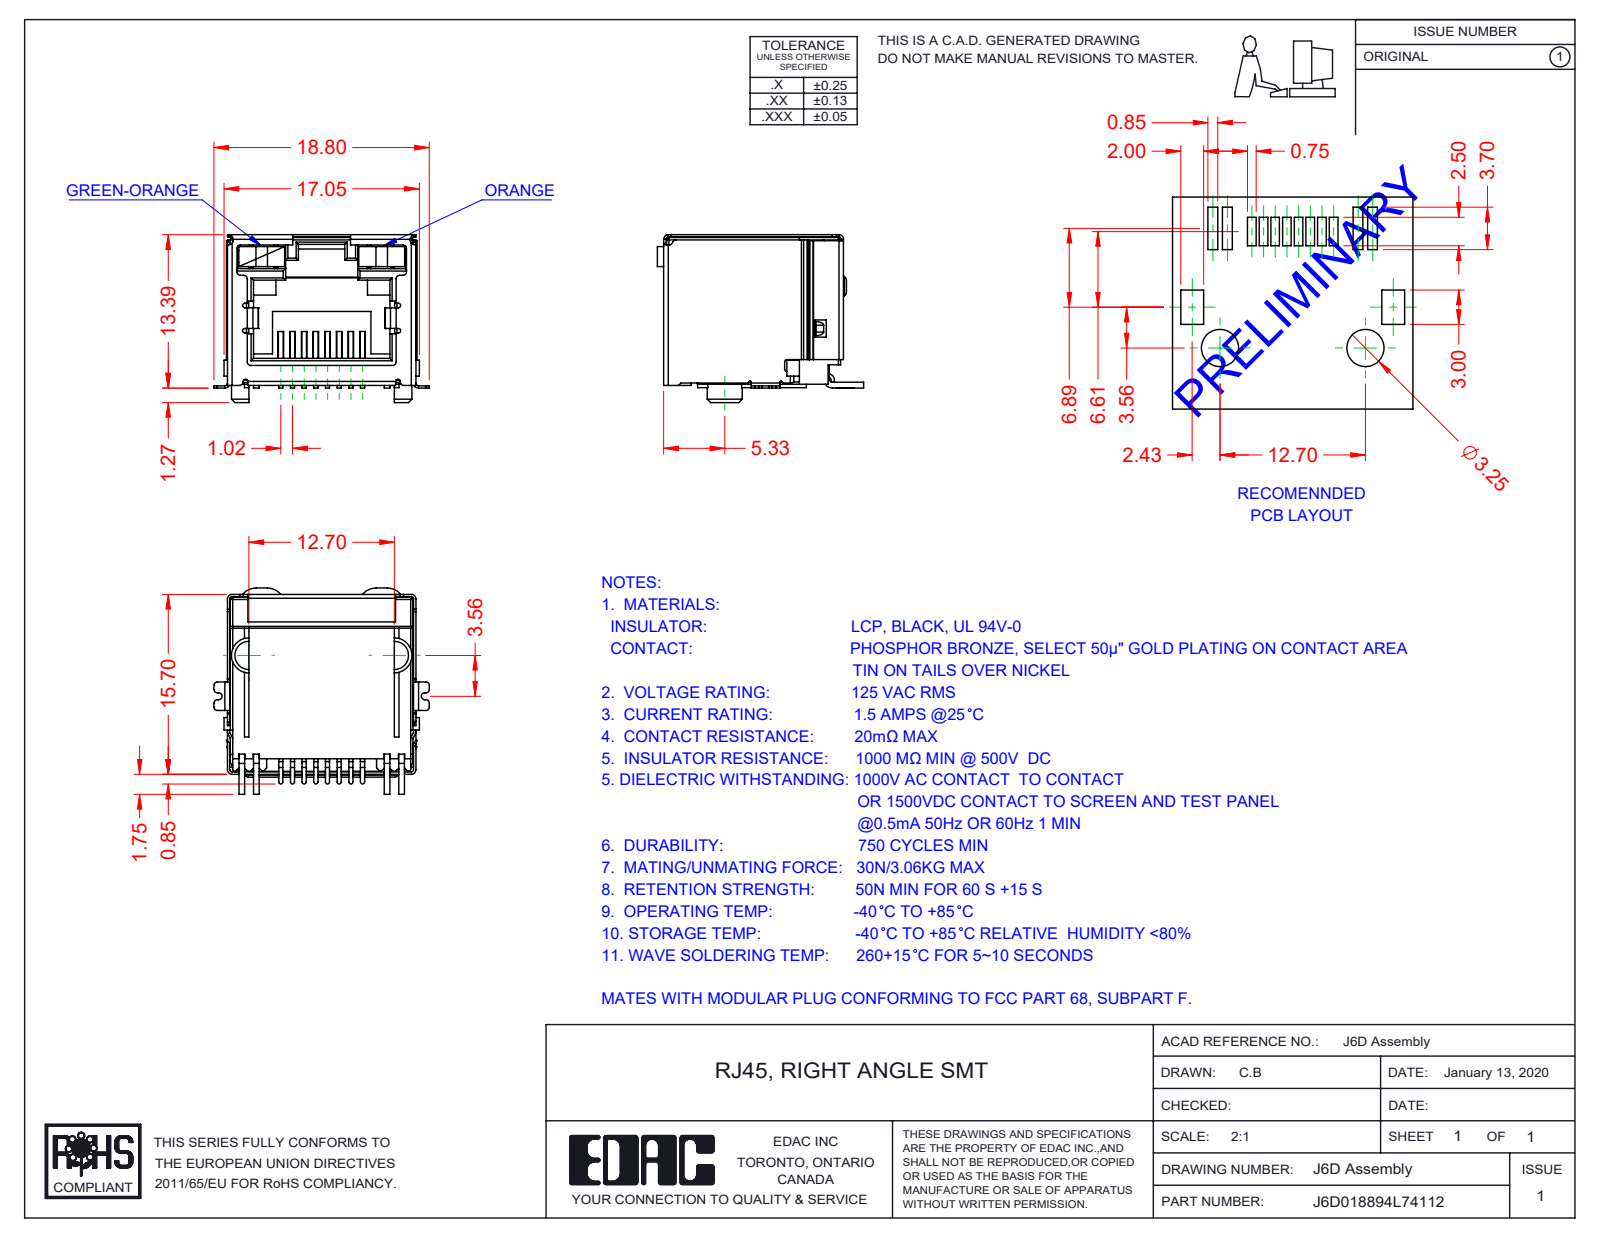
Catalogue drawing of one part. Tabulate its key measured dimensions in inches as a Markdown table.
| quantity | value |
| --- | --- |
| part name | 6D Contacts; J6D018894L74112; 6D Shield_LED - No EMI; 6D Insulator (+2 more) |
| STEP written by | SolidWorks 2016 (CONFIG_CONTROL_DESIGN) |
| units | inches |
| bodies | 12 solids, 896 faces (645 planar, 218 cylindrical, 33 other) |
| overall size | 0.74 × 0.709 × 0.577 |
| volume | 0.11 in³ |
| surface area | 7.592 in² |
| partial cylindrical surfaces (radius × count) | 0.012 × 39, 0.008 × 37, 0.016 × 16, 0.004 × 12, 0.006 × 8, 0.007 × 8, 0.02 × 6, 0.059 × 5 |
| main face-to-face distances | 0.63, 0.64, 0.638, 0.089, 0.039, 0.628, 0.632, 0.504, 0.018, 0.648 |
